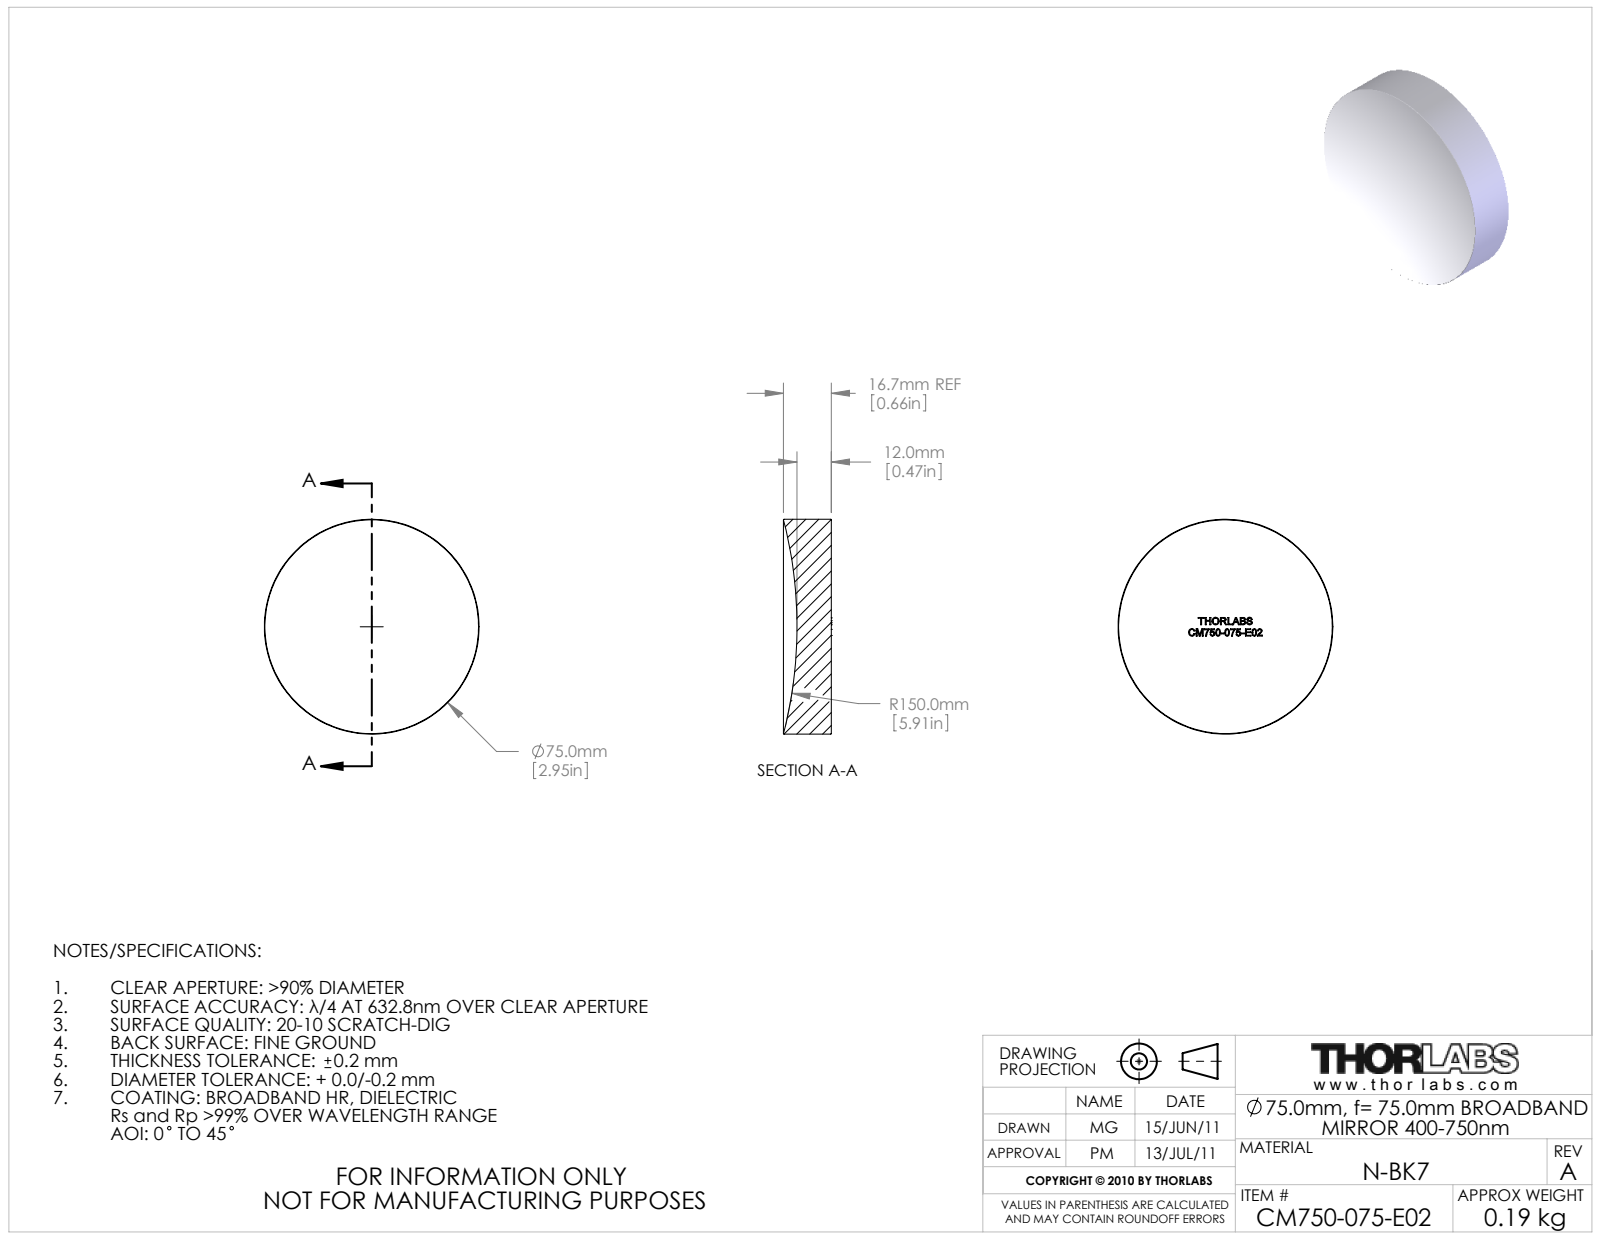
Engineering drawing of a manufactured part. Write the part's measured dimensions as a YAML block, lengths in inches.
part_name: "22634-E0W"
step_written_by: "SolidWorks 2011 (AUTOMOTIVE_DESIGN)"
units: inches
bodies: {solids: 0, faces: 38, planar: 30, cylindrical: 2, other: 6}
overall_size: [2.953, 2.953, 0.658]
round_bosses_or_shafts:
  - {diameter: 2.953, count: 1}
